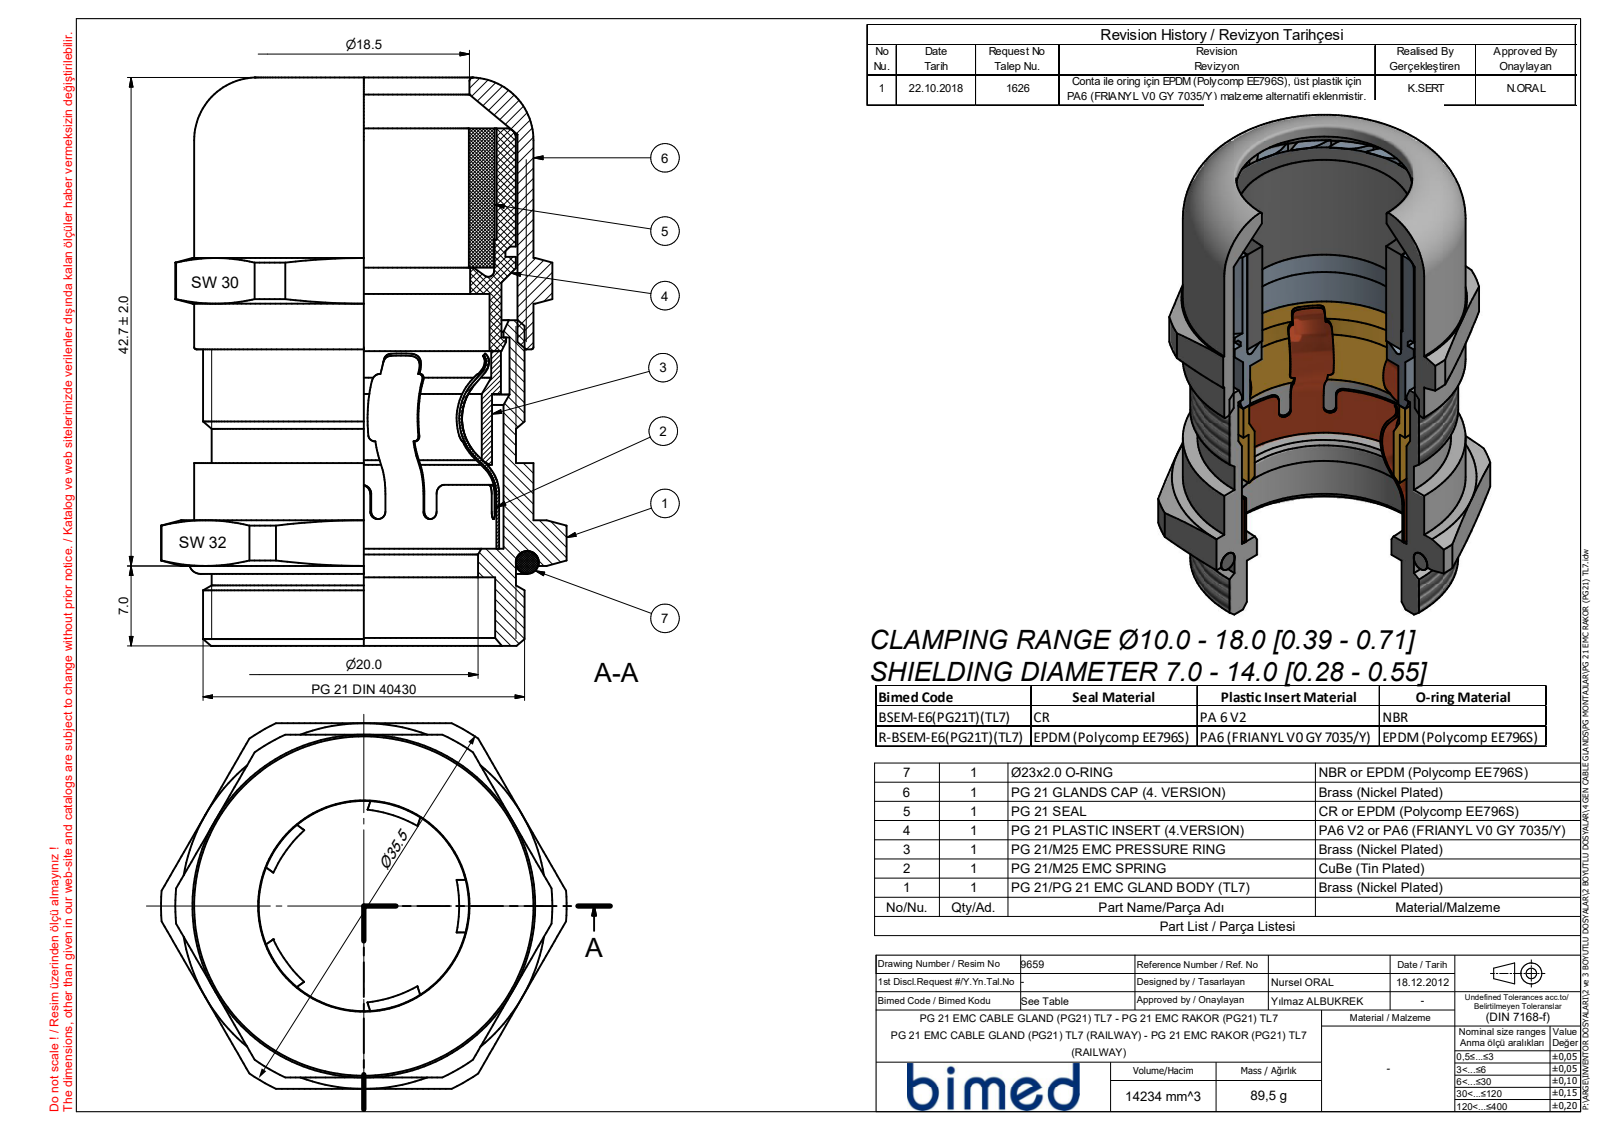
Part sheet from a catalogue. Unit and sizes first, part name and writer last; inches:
Units: inches
Overall size (bounding box): 1.959 × 1.398 × 1.26
Round bosses / shafts (diameter × count): ⌀1.169 ×1, ⌀1.108 ×1, ⌀1.048 ×1
Partial cylindrical surfaces — rounded edges, fillets, slot ends (radius × count): R0.65 ×1, R0.699 ×1
Main face-to-face distances: 0.039, 1.22, 1.949, 1.26, 1.181, 0.63, 1.319, 0.433, 0.197, 1.516
Volume: 2.039 in³ · Surface area: 10.24 in²
Bodies: 1 solid, 91 faces (21 planar, 28 cylindrical, 42 other)
Part name (STEP PRODUCT): BSEM-E6-PG21T-WCL
STEP written by: SolidWorks 2021 (CONFIG_CONTROL_DESIGN)
